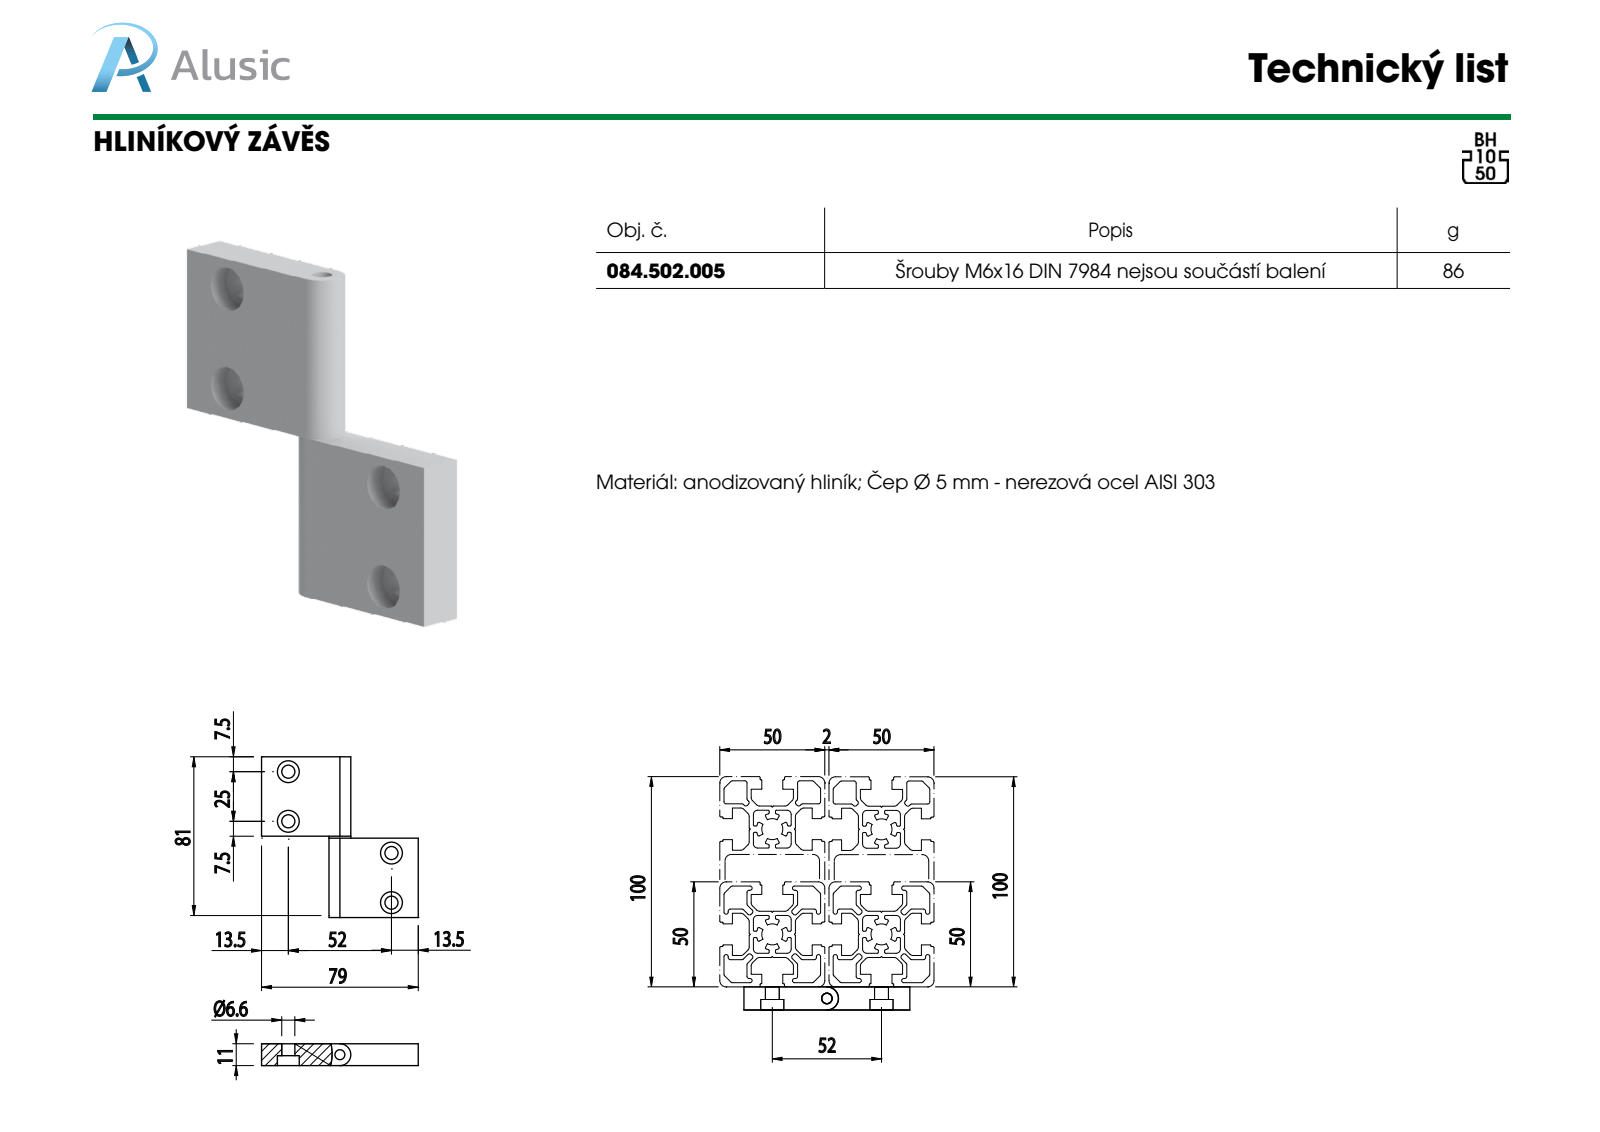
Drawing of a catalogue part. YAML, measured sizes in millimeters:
part_name: "084.502.000 ALETTE_ALETTA 3; 084.502.005"
step_written_by: "SolidWorks 2012 (CONFIG_CONTROL_DESIGN)"
units: millimeters
bodies: {solids: 2, faces: 36, planar: 14, cylindrical: 22, other: 0}
overall_size: [80, 79, 11]
volume: 34269
surface_area: 12604
round_holes:
  - {diameter: 6.6, count: 4}
  - {diameter: 11, count: 4}
  - {diameter: 5, count: 1}
round_bosses_or_shafts:
  - {diameter: 11, count: 1}
face_to_face_distances: [11, 40, 80, 79, 6, 5]
hole_center_spacings: [25, 65.6, 54.12, 83.24]
